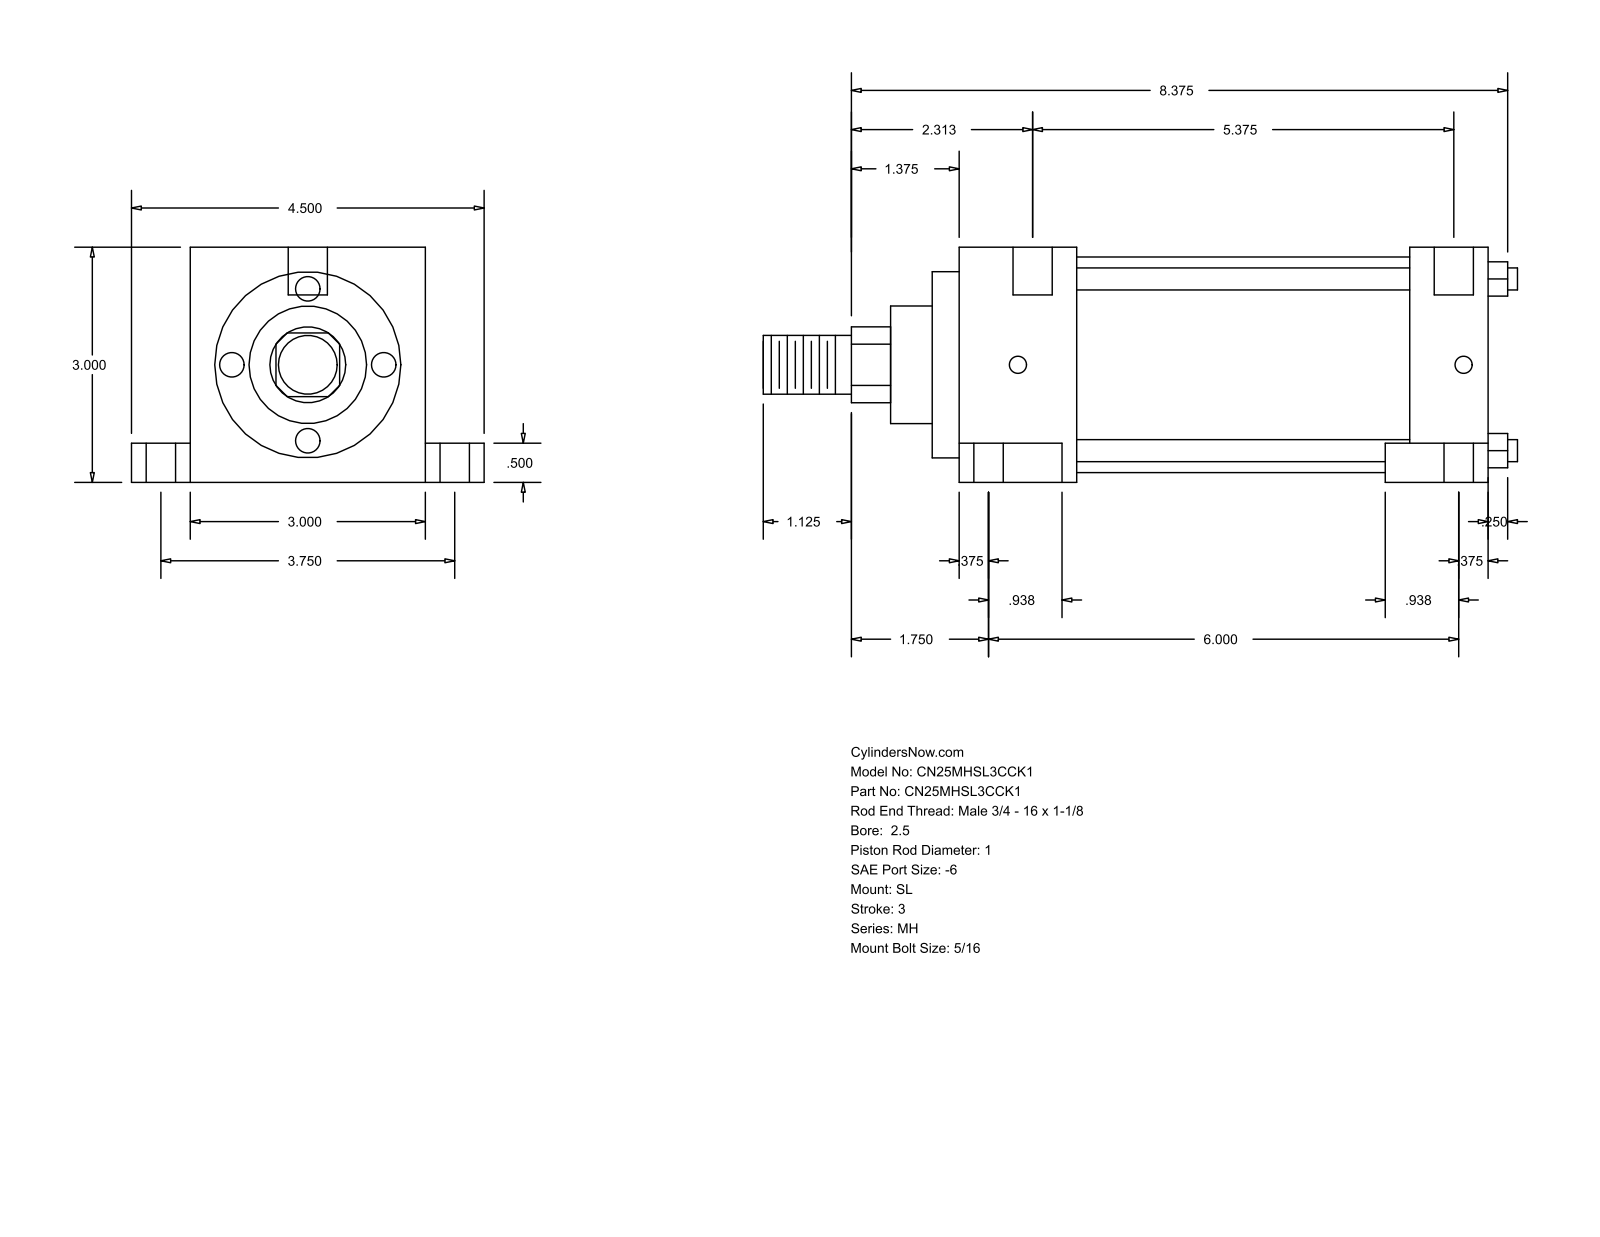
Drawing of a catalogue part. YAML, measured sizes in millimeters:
part_name: "MH_SL__0250_1"
step_written_by: "GSSL Pune (CONFIG_CONTROL_DESIGN)"
units: millimeters
bodies: {solids: 0, faces: 86, planar: 61, cylindrical: 25, other: 0}
overall_size: [244.47, 114.3, 76.2]
round_holes:
  - {diameter: 5.56, count: 2}
  - {diameter: 9.53, count: 2}
  - {diameter: 15.88, count: 2}
  - {diameter: 12.7, count: 1}
round_bosses_or_shafts:
  - {diameter: 7.14, count: 4}
  - {diameter: 69.85, count: 1}
  - {diameter: 60.33, count: 1}
  - {diameter: 38.1, count: 1}
  - {diameter: 25.4, count: 1}
  - {diameter: 19.05, count: 1}
partial_cylinders:
  - {radius: 12.29, count: 1}
face_to_face_distances: [76.2, 25.41, 154.78, 180.19, 12.7, 63.5, 19.05, 95.25, 13.49, 168.27]
hole_center_spacings: [47.65, 3.18, 95.24]
